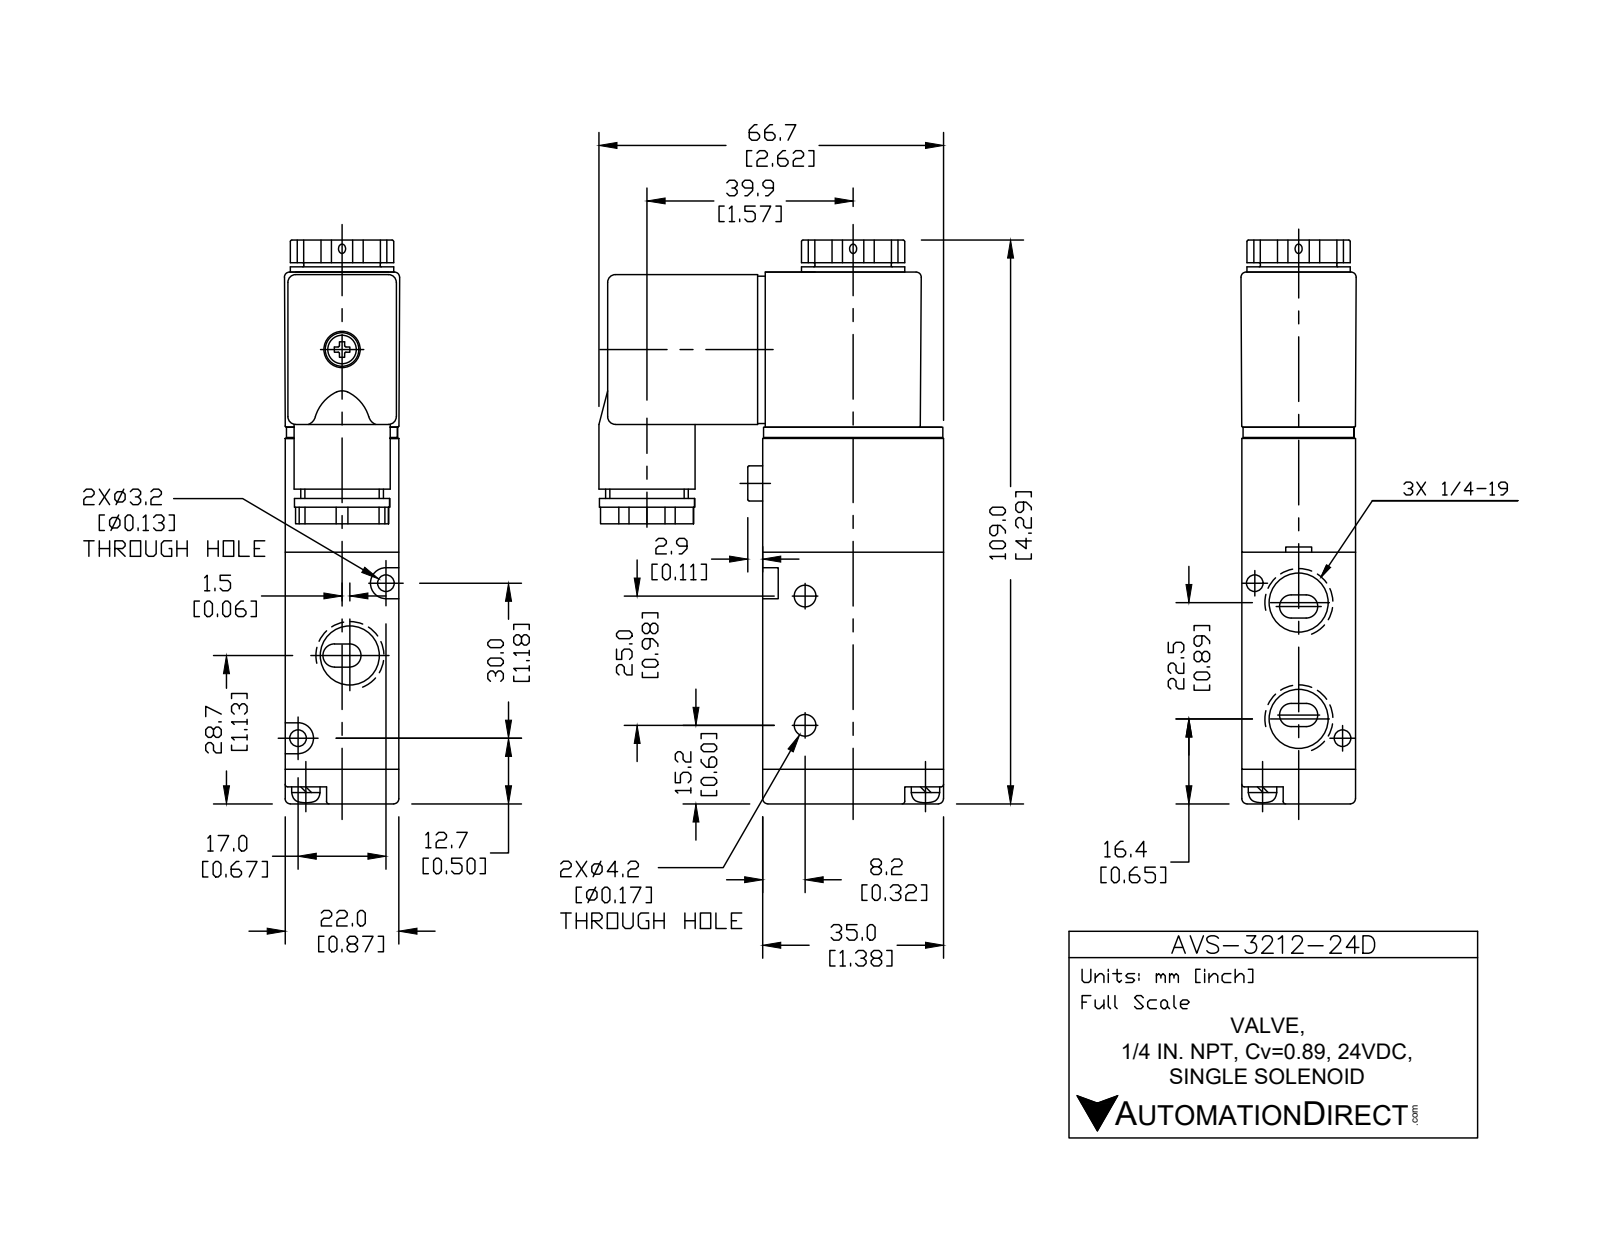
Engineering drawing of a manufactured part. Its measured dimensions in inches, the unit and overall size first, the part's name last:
Units: inches
Overall size (bounding box): 4.295 × 2.626 × 0.866
Round holes (diameter × count): ⌀0.438 ×3, ⌀0.13 ×2, ⌀0.169 ×2, ⌀0.366 ×1
Round bosses / shafts (diameter × count): ⌀0.787 ×1, ⌀0.732 ×1, ⌀0.724 ×1, ⌀0.63 ×1, ⌀0.583 ×1, ⌀0.268 ×1
Partial cylindrical surfaces — rounded edges, fillets, slot ends (radius × count): R0.02 ×11, R0.039 ×10, R0.118 ×2
Main face-to-face distances: 0.02, 0.846, 1.654, 0.866, 0.264, 1.917, 4.031, 0.827, 1.181, 3.768
Hole centre spacings: 0.365, 0.367, 0.41, 0.484, 0.616, 0.743, 0.886, 0.984
Volume: 5.732 in³ · Surface area: 36.98 in²
Bodies: 4 solids, 159 faces (84 planar, 53 cylindrical, 22 other)
Part name (STEP PRODUCT): AVS-3212-24D
STEP written by: SolidWorks 2015 (CONFIG_CONTROL_DESIGN)
